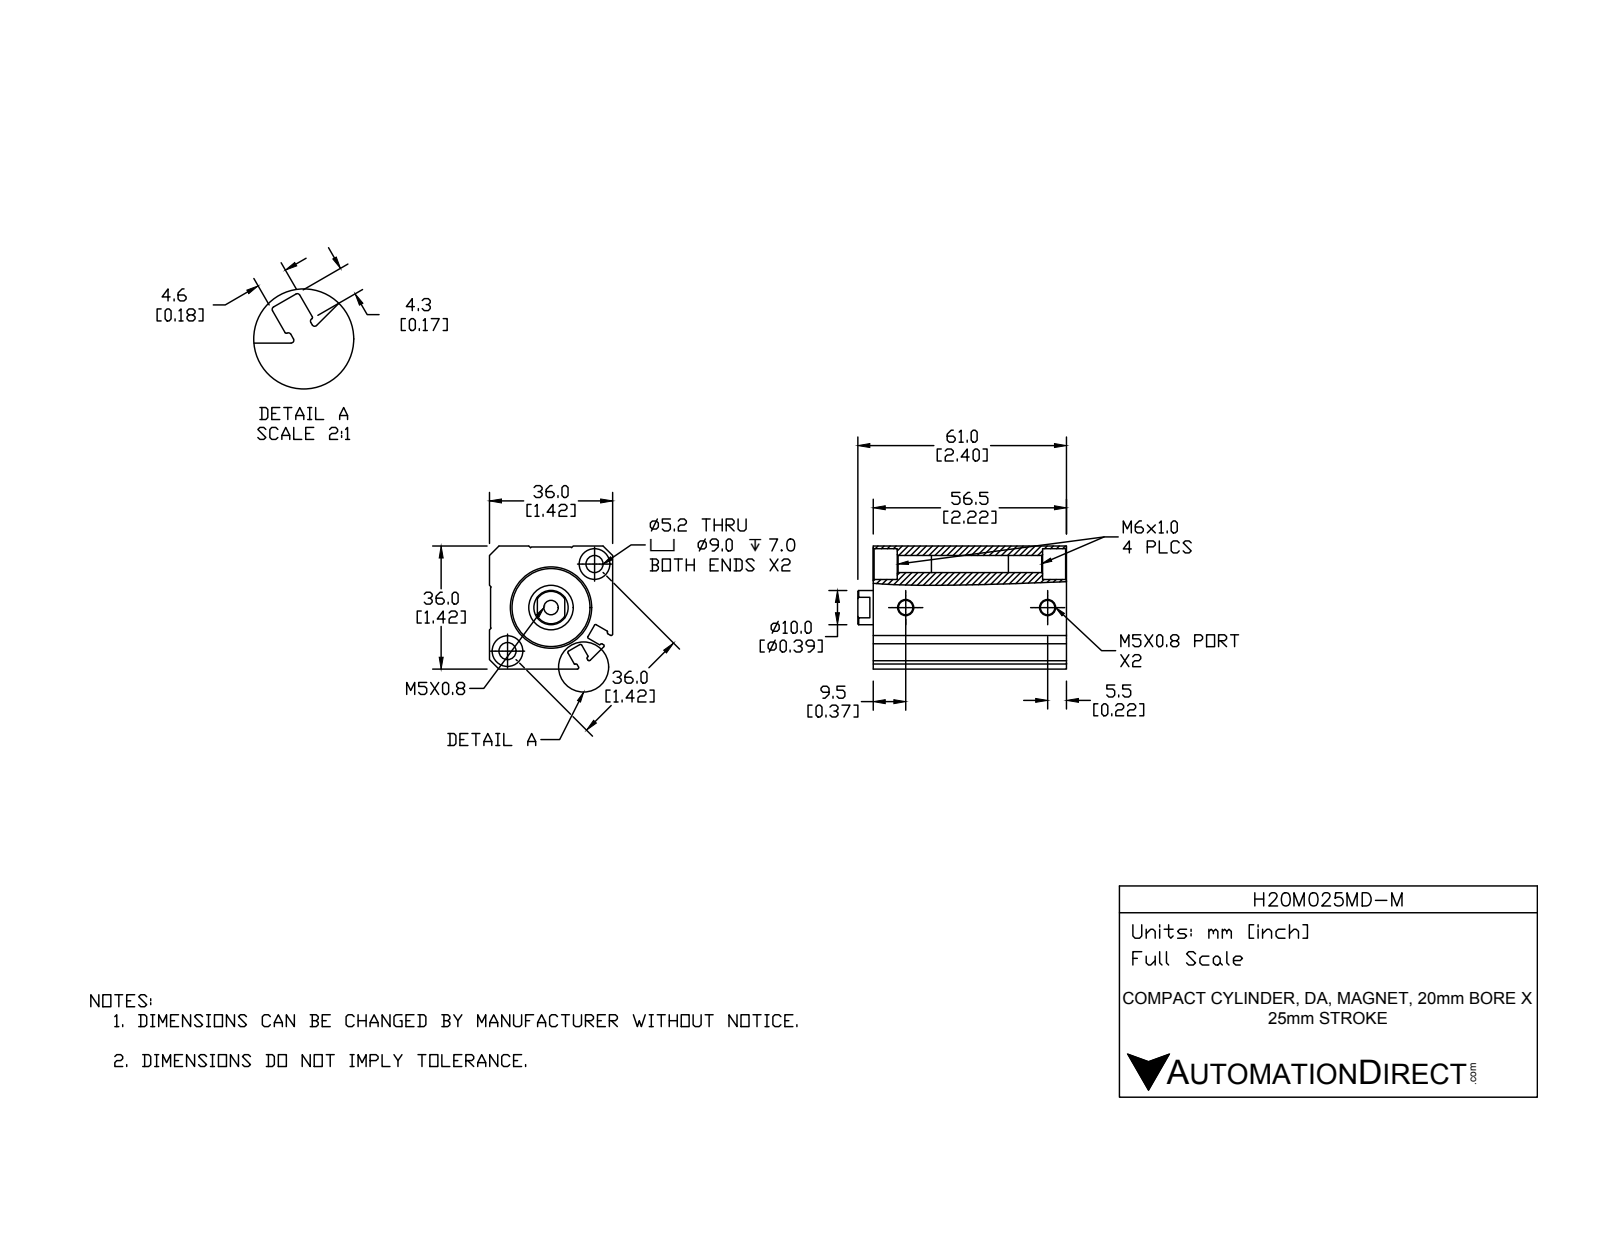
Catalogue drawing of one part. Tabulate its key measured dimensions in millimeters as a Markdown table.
| quantity | value |
| --- | --- |
| part name | H20M025MD-M-PISTON; H20M025MD-M; H20M025MD-M-BODY |
| STEP written by | SolidWorks 2015 (CONFIG_CONTROL_DESIGN) |
| units | millimeters |
| bodies | 2 solids, 141 faces (53 planar, 55 cylindrical, 33 other) |
| overall size | 61 × 36 × 36 |
| volume | 56 295 mm³ |
| surface area | 20 452 mm² |
| round holes (diameter × count) | 4.2 × 3, 5 × 2, 9 × 2, 10 × 1, 13 × 1, 20 × 1, 22.8 × 1 |
| round bosses / shafts (diameter × count) | 11 × 1 |
| partial cylindrical surfaces (radius × count) | 0.4 × 12, 0.2 × 4 |
| main face-to-face distances | 36, 35.7, 4, 56.5, 52.5, 2.6, 4.6, 1.4, 55.1, 45.5 |
| hole center spacings | 18, 36.01, 41.5 |
